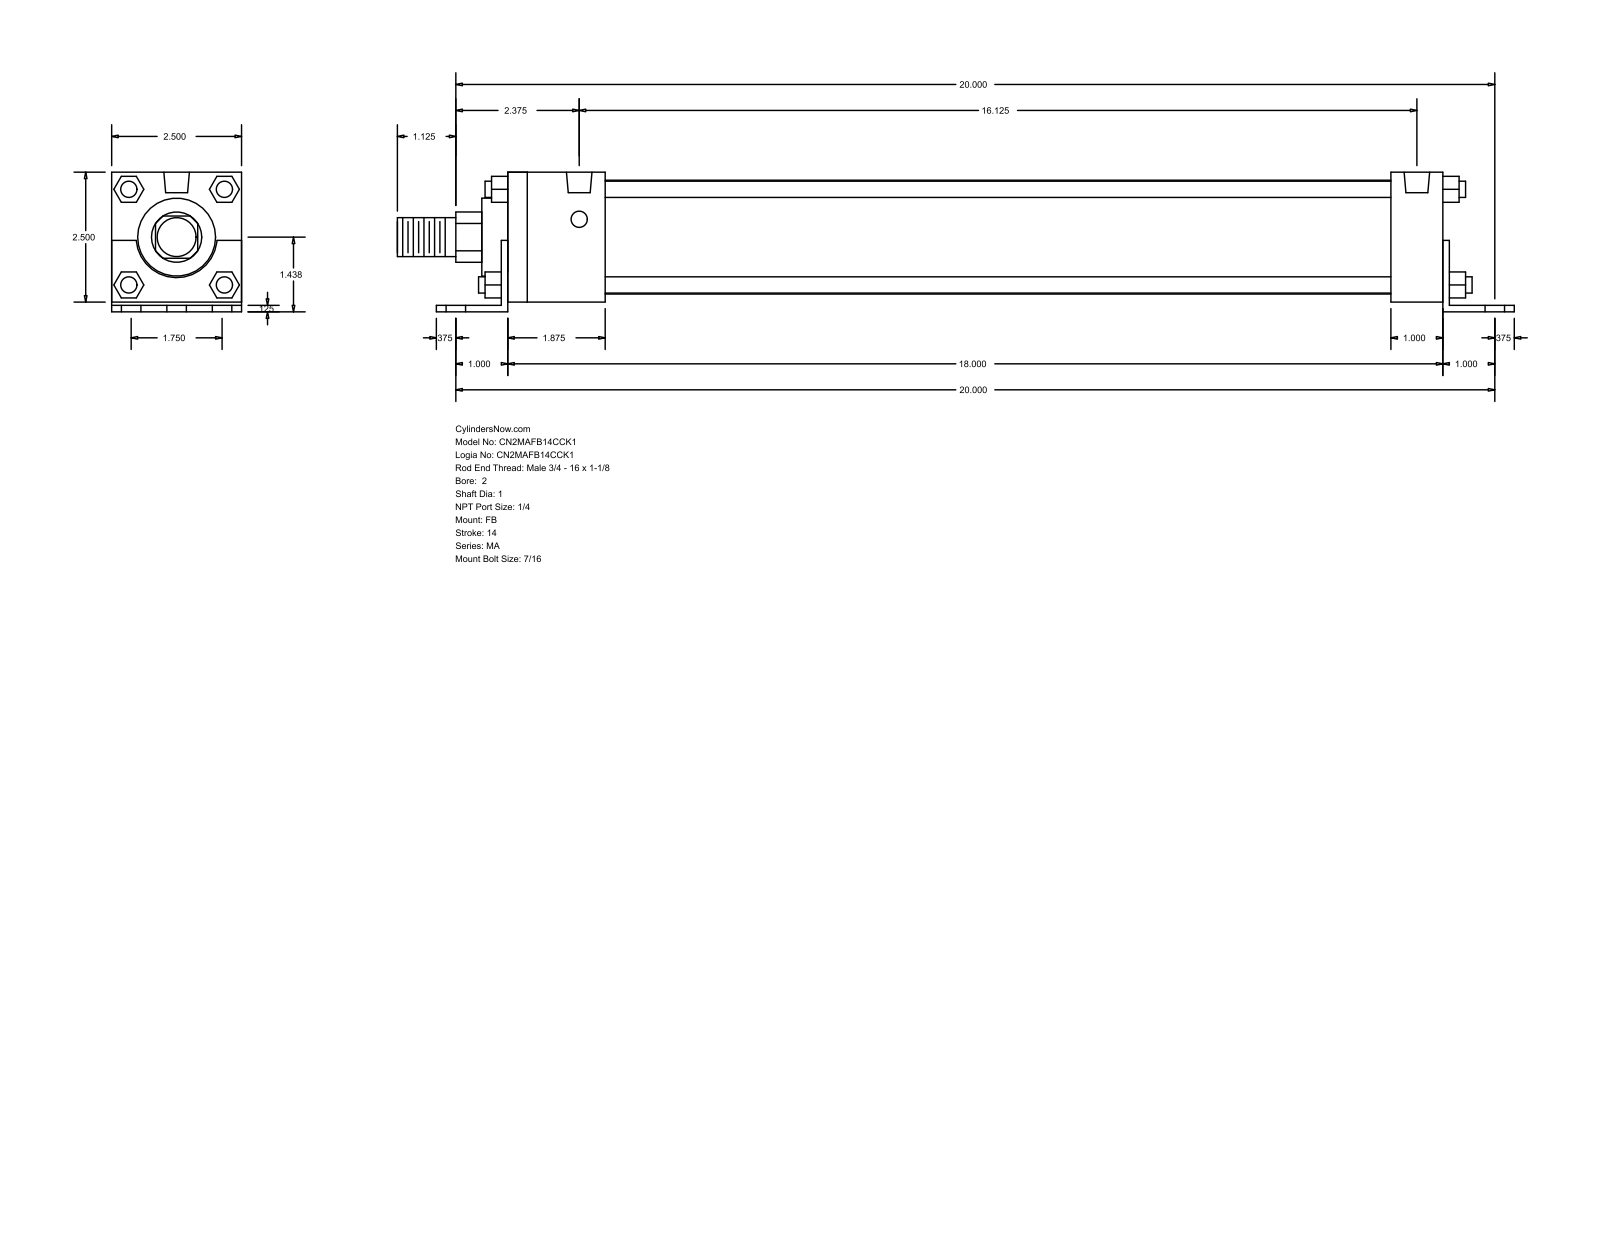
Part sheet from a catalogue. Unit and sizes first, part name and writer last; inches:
Units: inches
Overall size (bounding box): 21.5 × 2.687 × 2.5
Round holes (diameter × count): ⌀0.437 ×6, ⌀0.313 ×4, ⌀0.492 ×2
Round bosses / shafts (diameter × count): ⌀0.313 ×4, ⌀2.19 ×1, ⌀1.5 ×1, ⌀1 ×1, ⌀0.75 ×1
Partial cylindrical surfaces — rounded edges, fillets, slot ends (radius × count): R0.484 ×1, R0.78 ×1
Main face-to-face distances: 2.5, 0.125, 0.187, 2.687, 0.063, 2.563, 18.125, 0.5, 18, 1.125
Hole centre spacings: 0.875, 20.019, 20, 1.737, 1.75, 2.531, 16.125, 17.646
Bodies: 0 solids, 140 faces (105 planar, 35 cylindrical, 0 other)
Part name (STEP PRODUCT): MA_FB__0200_1
STEP written by: GSSL Pune (CONFIG_CONTROL_DESIGN)
